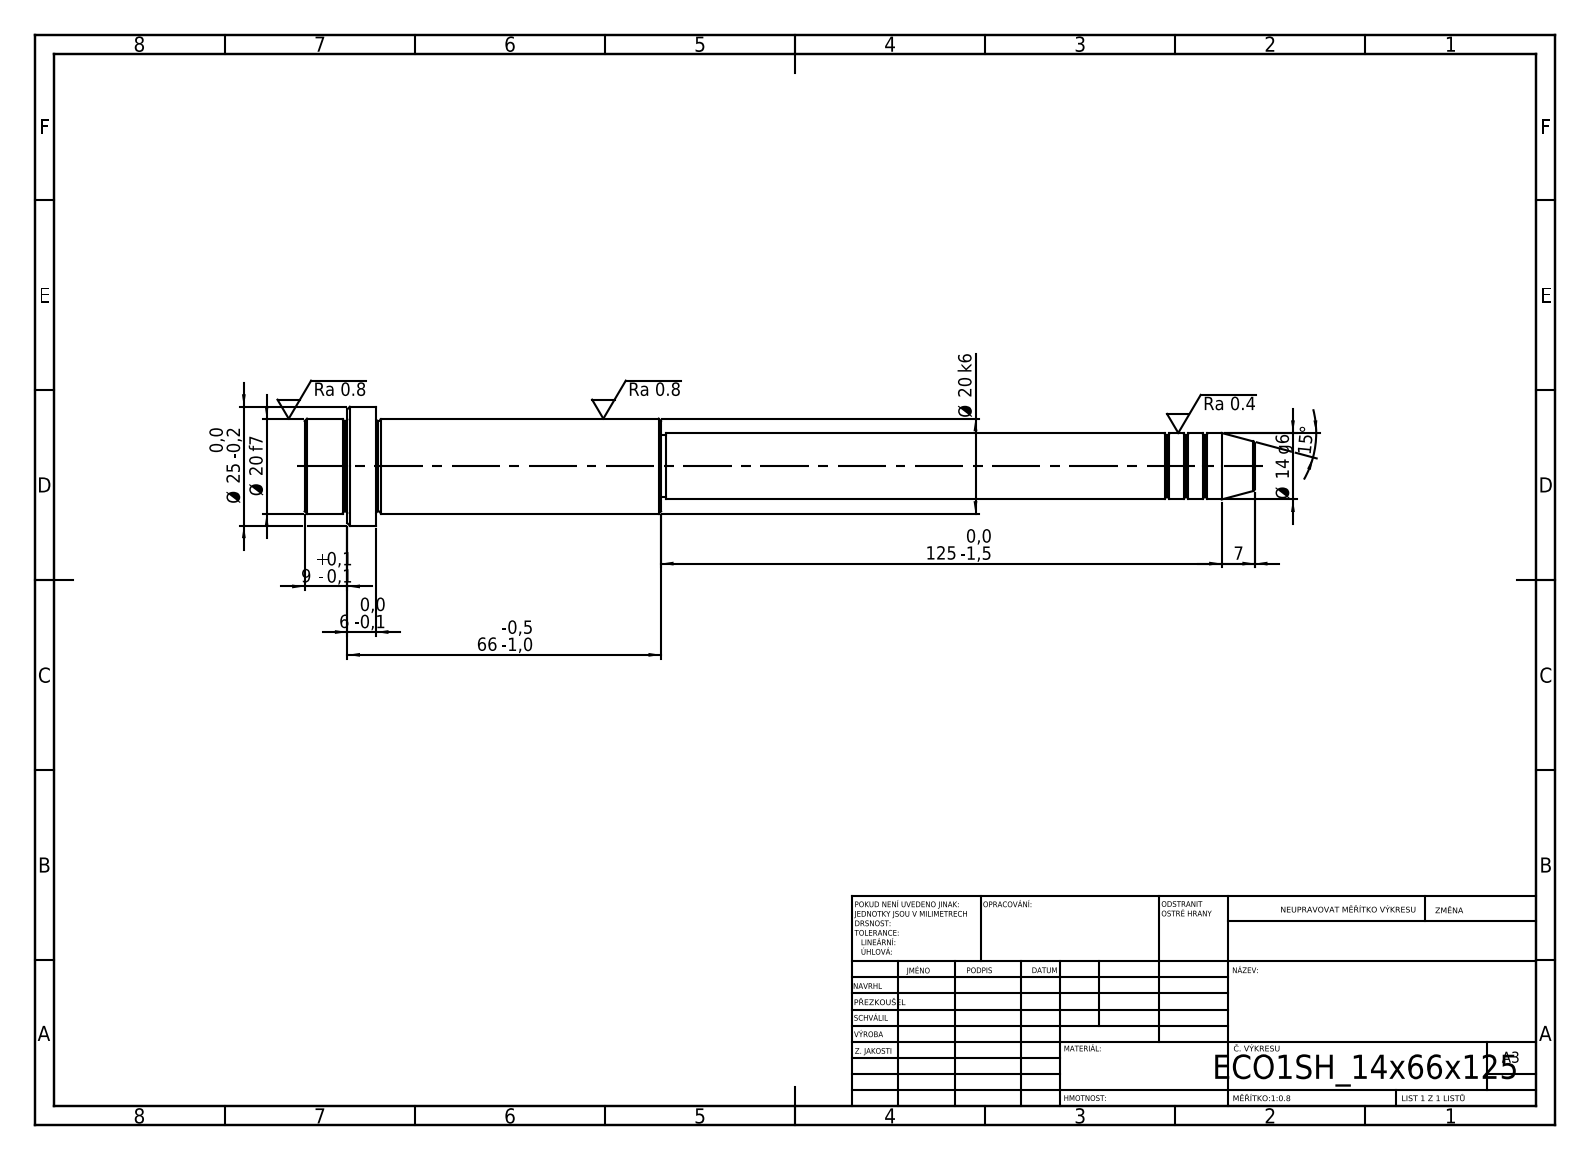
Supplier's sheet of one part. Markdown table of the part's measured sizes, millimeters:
| quantity | value |
| --- | --- |
| STEP written by | SolidWorks 2019 (CONFIG_CONTROL_DESIGN) |
| units | millimeters |
| bodies | 1 solid, 52 faces (6 planar, 16 cylindrical, 30 other) |
| overall size | 200 × 25 × 25 |
| volume | 43 456 mm³ |
| surface area | 11 289 mm² |
| round bosses / shafts (diameter × count) | 25 × 1, 20 × 1, 14 × 1, 13 × 1 |
| main face-to-face distances | 15, 60, 75, 66, 6, 9, 125, 185, 191, 200 |
